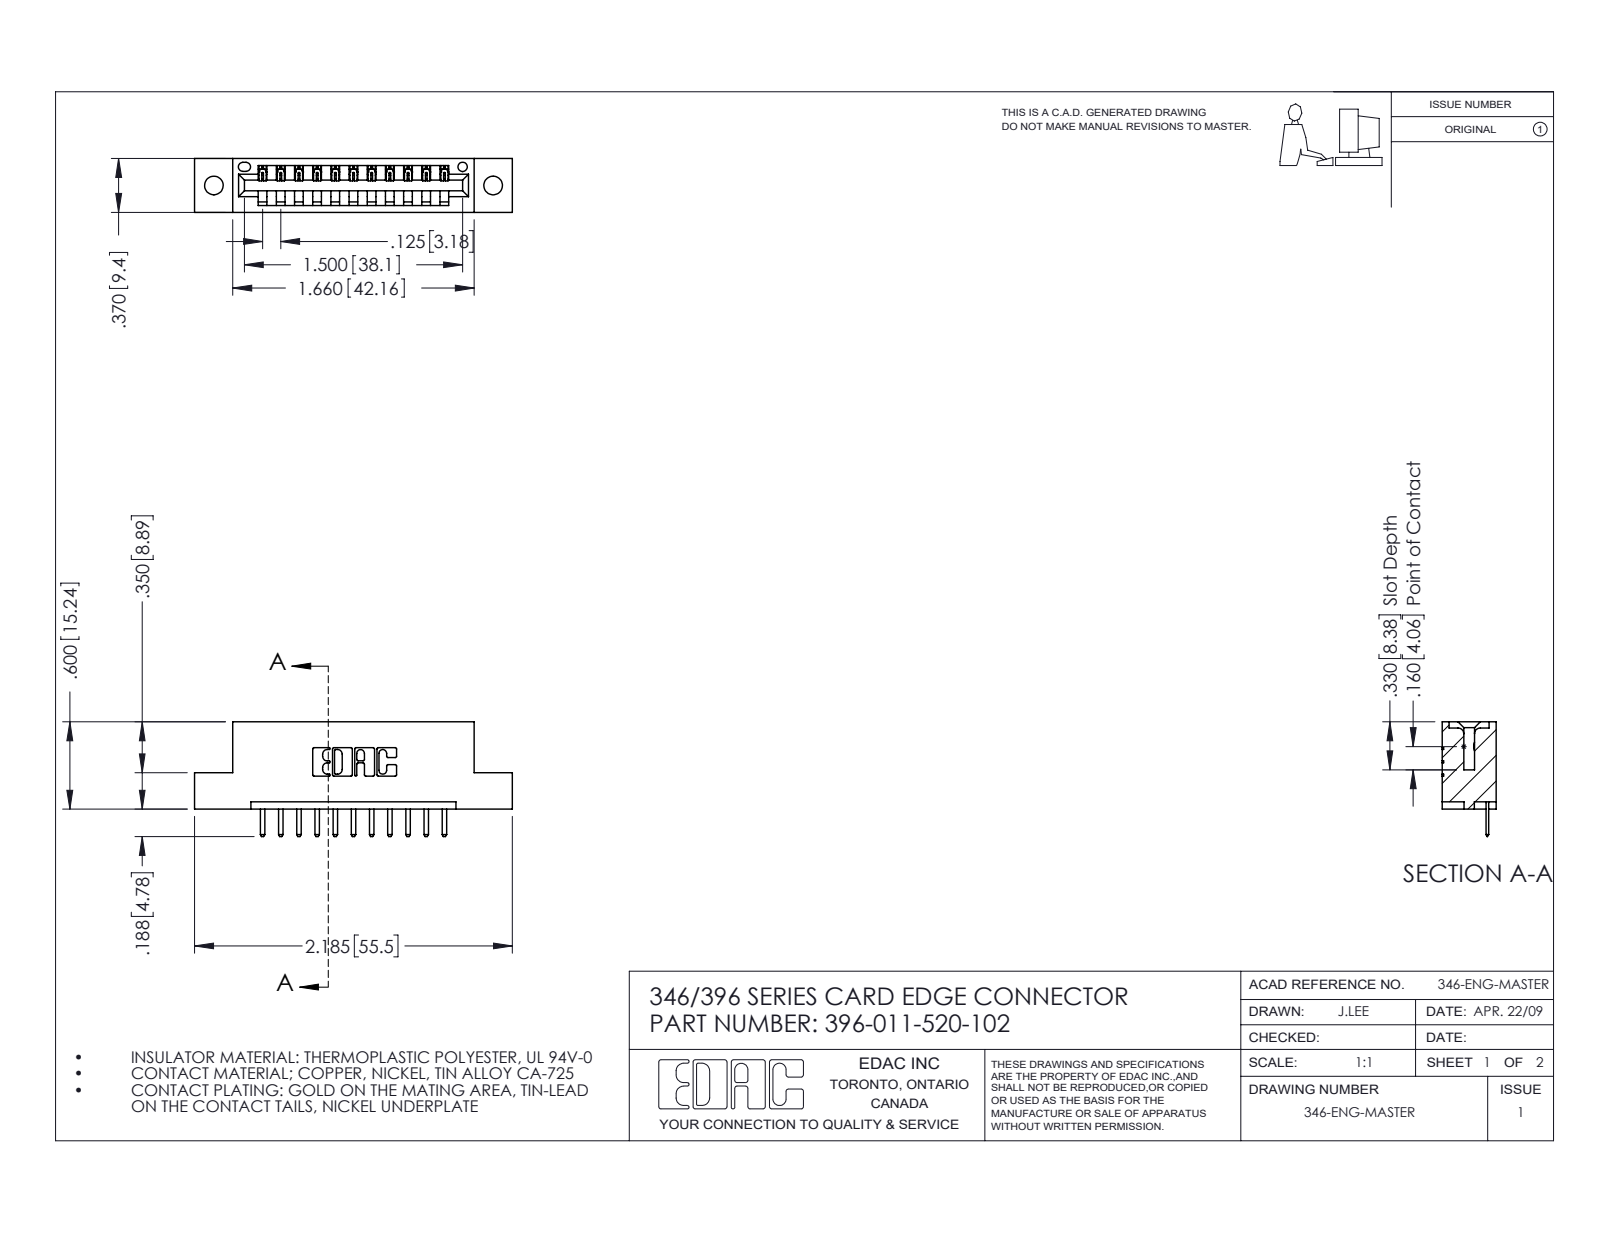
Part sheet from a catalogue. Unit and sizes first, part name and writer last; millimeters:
Units: millimetres
Overall size (bounding box): 55.5 × 20 × 9.4
Round holes (diameter × count): ⌀3.3 ×2, ⌀1.6 ×1
Partial cylindrical surfaces — rounded edges, fillets, slot ends (radius × count): R0.3 ×24, R0.2 ×22, R0.3 ×22, R0.2 ×6, R0.8 ×6, R0.7 ×3, R0.8 ×2, R1 ×2
Main face-to-face distances: 6.4, 9.4, 1.2, 8.2, 3.8, 5.6, 2.5, 4.4, 1.8, 7.6
Hole centre spacings: 6.2, 43.6, 48.8
Volume: 5 030 mm³ · Surface area: 5 576 mm²
Bodies: 12 solids, 804 faces (538 planar, 266 cylindrical, 0 other)
Part name (STEP PRODUCT): 346 Part_Flush Mounting Lugs - 0.128 Dia; 396-011-520-102; 345-292-001_345-293-120
STEP written by: SolidWorks 2016 (CONFIG_CONTROL_DESIGN)
